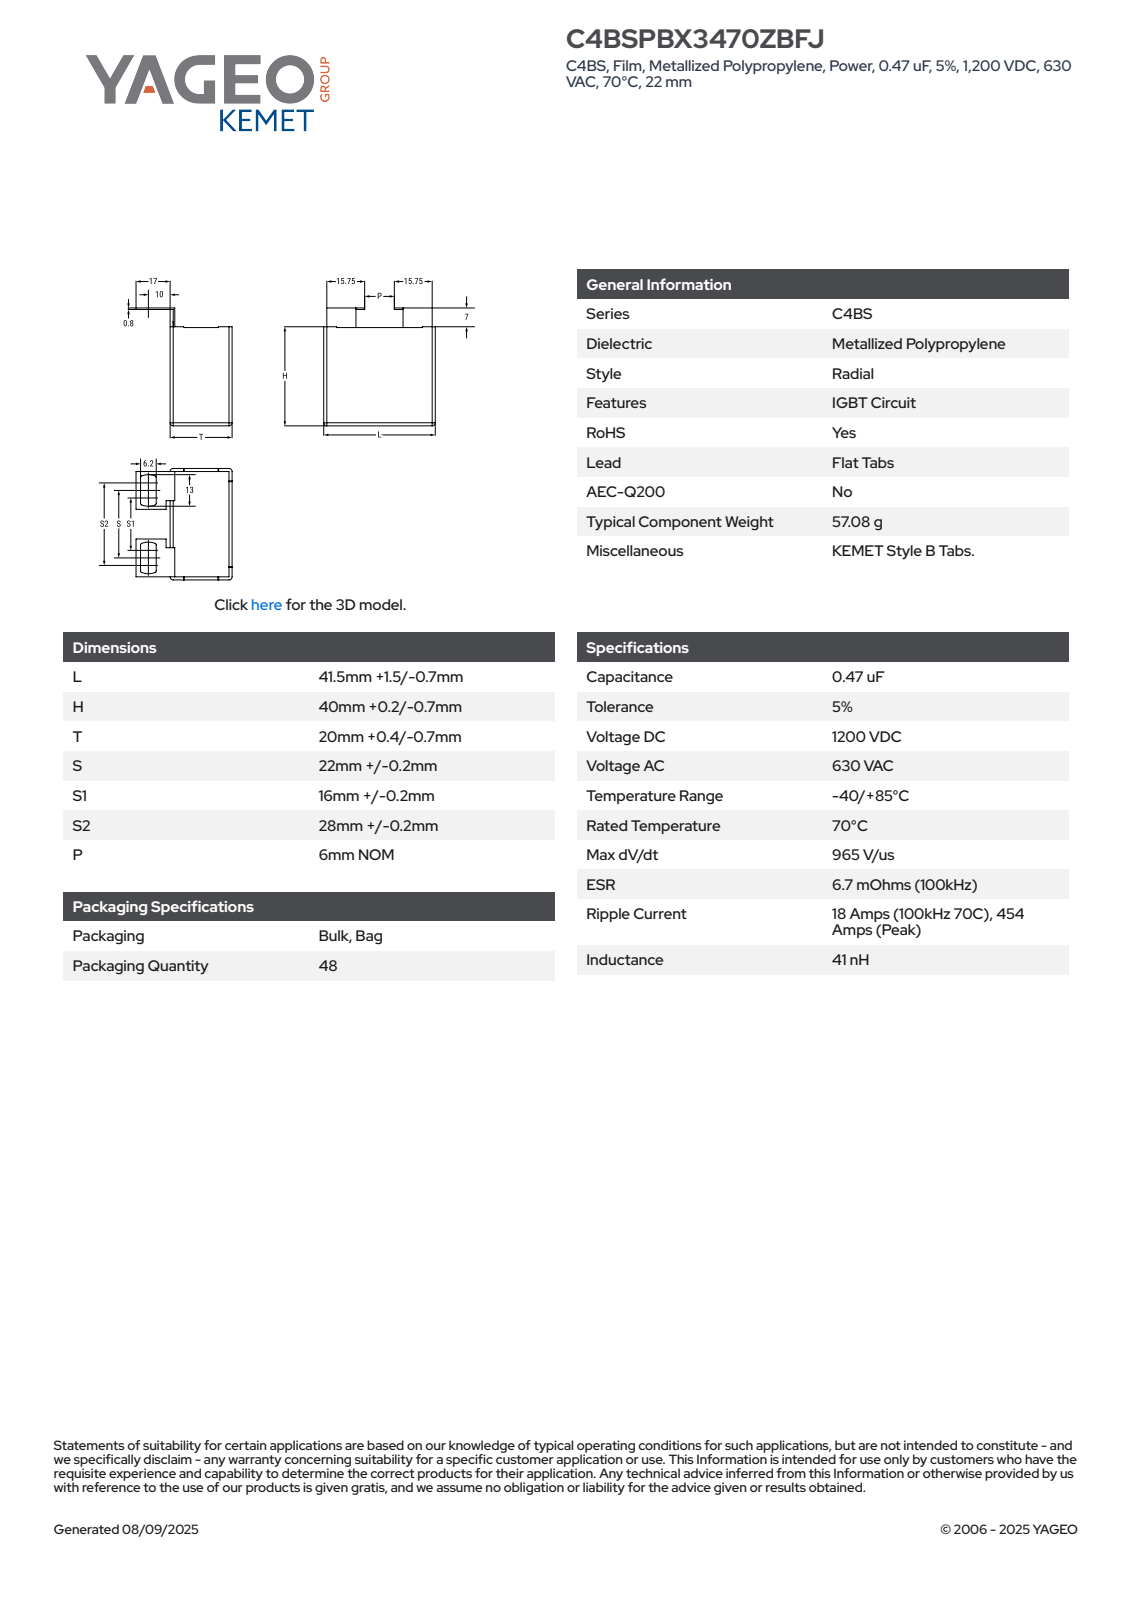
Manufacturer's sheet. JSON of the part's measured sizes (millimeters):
{"part_name": "CFP_C4BB_41.5X40X20_L43H40.2T20.4S22.2", "step_written_by": "SolidWorks 2014 (AUTOMOTIVE_DESIGN)", "units": "millimeters", "bodies": {"solids": 4, "faces": 93, "planar": 85, "cylindrical": 8, "other": 0}, "overall_size": [47.2, 43, 37.4], "volume_mm3": 35798, "surface_area_mm2": 8438, "partial_cylinders_radius": [[4.6, 4], [0.2, 2]], "face_to_face_distances": [20.4, 40.2, 43, 0.8, 7, 47.2, 6.2, 46.4, 18.4, 2]}
